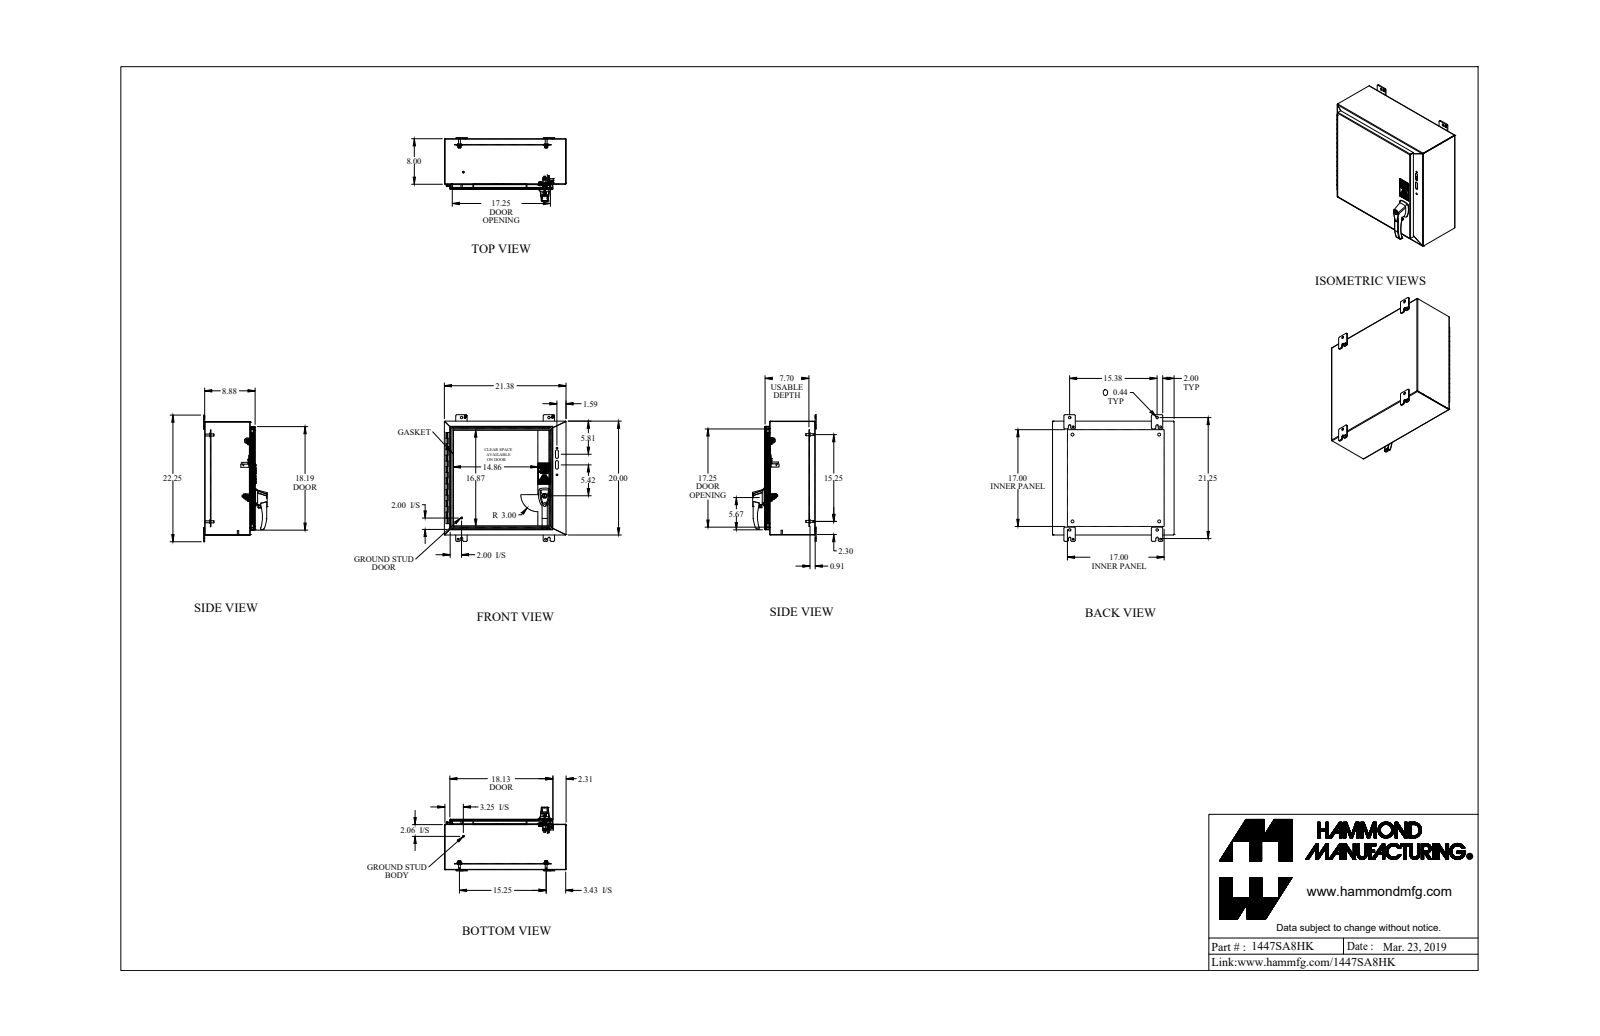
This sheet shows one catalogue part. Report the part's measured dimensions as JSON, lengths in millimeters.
{"part_name": "1447SA8HK", "step_written_by": "SolidWorks 2019 (AUTOMOTIVE_DESIGN)", "units": "millimeters", "bodies": {"solids": 49, "faces": 1178, "planar": 734, "cylindrical": 321, "other": 123}, "overall_size": [565.2, 542.9, 283.9], "volume_mm3": 2832000, "surface_area_mm2": 2761000, "round_holes": [[8, 5], [4.5, 4], [11.1, 4], [12.7, 4], [4, 2], [4.4, 2], [5.5, 2], [6.4, 2], [6.7, 2], [7.1, 2], [7.8, 2], [10.5, 2]], "round_bosses_or_shafts": [[9.5, 8], [6.4, 7], [25.4, 4], [16.5, 4], [8.4, 4], [4, 4], [12.7, 2], [10.2, 2]], "partial_cylinders_radius": [[4.8, 24], [6.4, 24], [0.9, 20], [2.7, 20], [3.2, 9], [5.5, 8], [1.5, 7], [0.8, 6]], "face_to_face_distances": [1.8, 223.6, 221.8, 506.2, 225.4, 541.1, 2.4, 197.4, 195.6, 26.2], "hole_center_spacings": [387.4, 390.5, 547.8, 466.7, 28.2, 44.1, 44.1, 47.1]}
